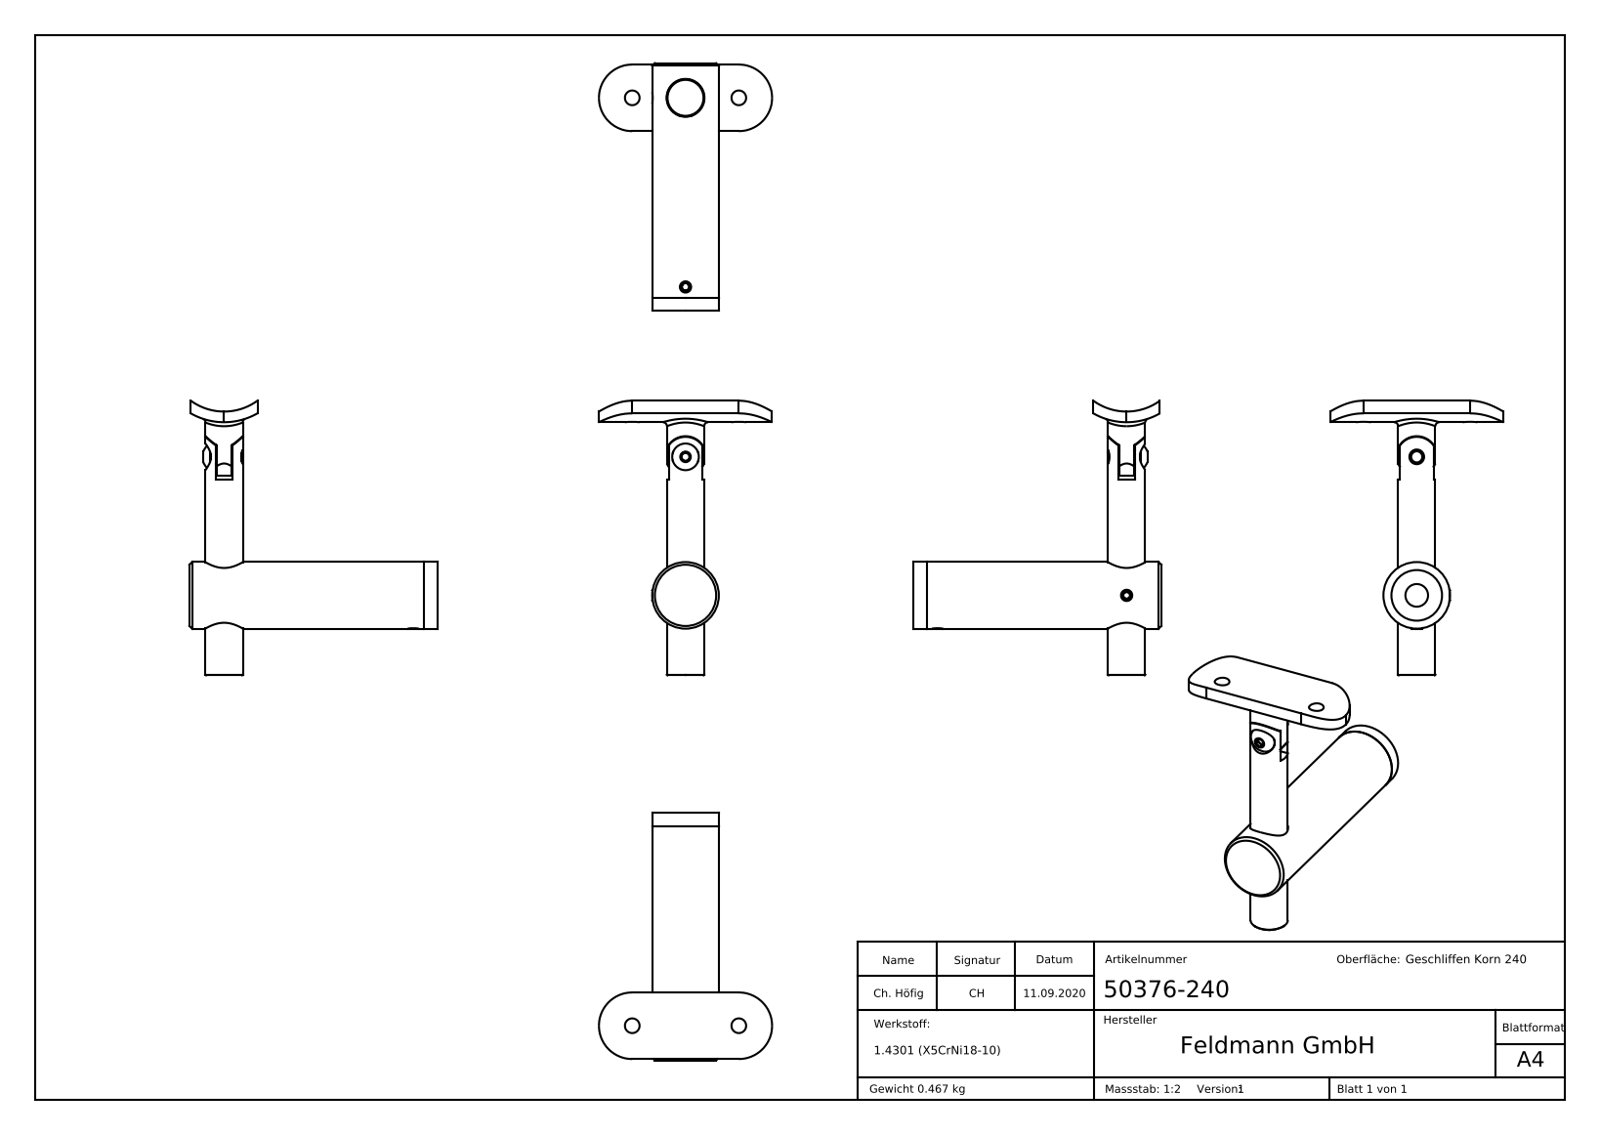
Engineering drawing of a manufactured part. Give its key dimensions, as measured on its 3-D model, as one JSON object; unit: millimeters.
{"part_name": "5037X-240 Teil3_50376-240 Teil3; DIN 7380; 5037X-240 Teil4_50374-240 Teil4; 5037X-240 Teil3 (+8 more)", "step_written_by": "SolidWorks 2018 (CONFIG_CONTROL_DESIGN)", "units": "millimeters", "bodies": {"solids": 7, "faces": 368, "planar": 144, "cylindrical": 80, "other": 144}, "overall_size": [103.08, 93, 88], "volume_mm3": 59053, "surface_area_mm2": 21988, "round_holes": [[4.2, 3], [5.5, 3], [8.5, 1], [10, 1], [14.2, 1], [16, 1], [19, 1]], "round_bosses_or_shafts": [[5, 3], [25, 1], [14, 1]], "partial_cylinders_radius": [[7.75, 3], [12.5, 2], [8.1, 1], [21.2, 1], [25.2, 1]], "face_to_face_distances": [88, 9.5, 15.5, 9.75, 5.75, 2, 15.25, 83, 3, 91], "hole_center_spacings": [20, 73.76, 40, 52, 71]}
